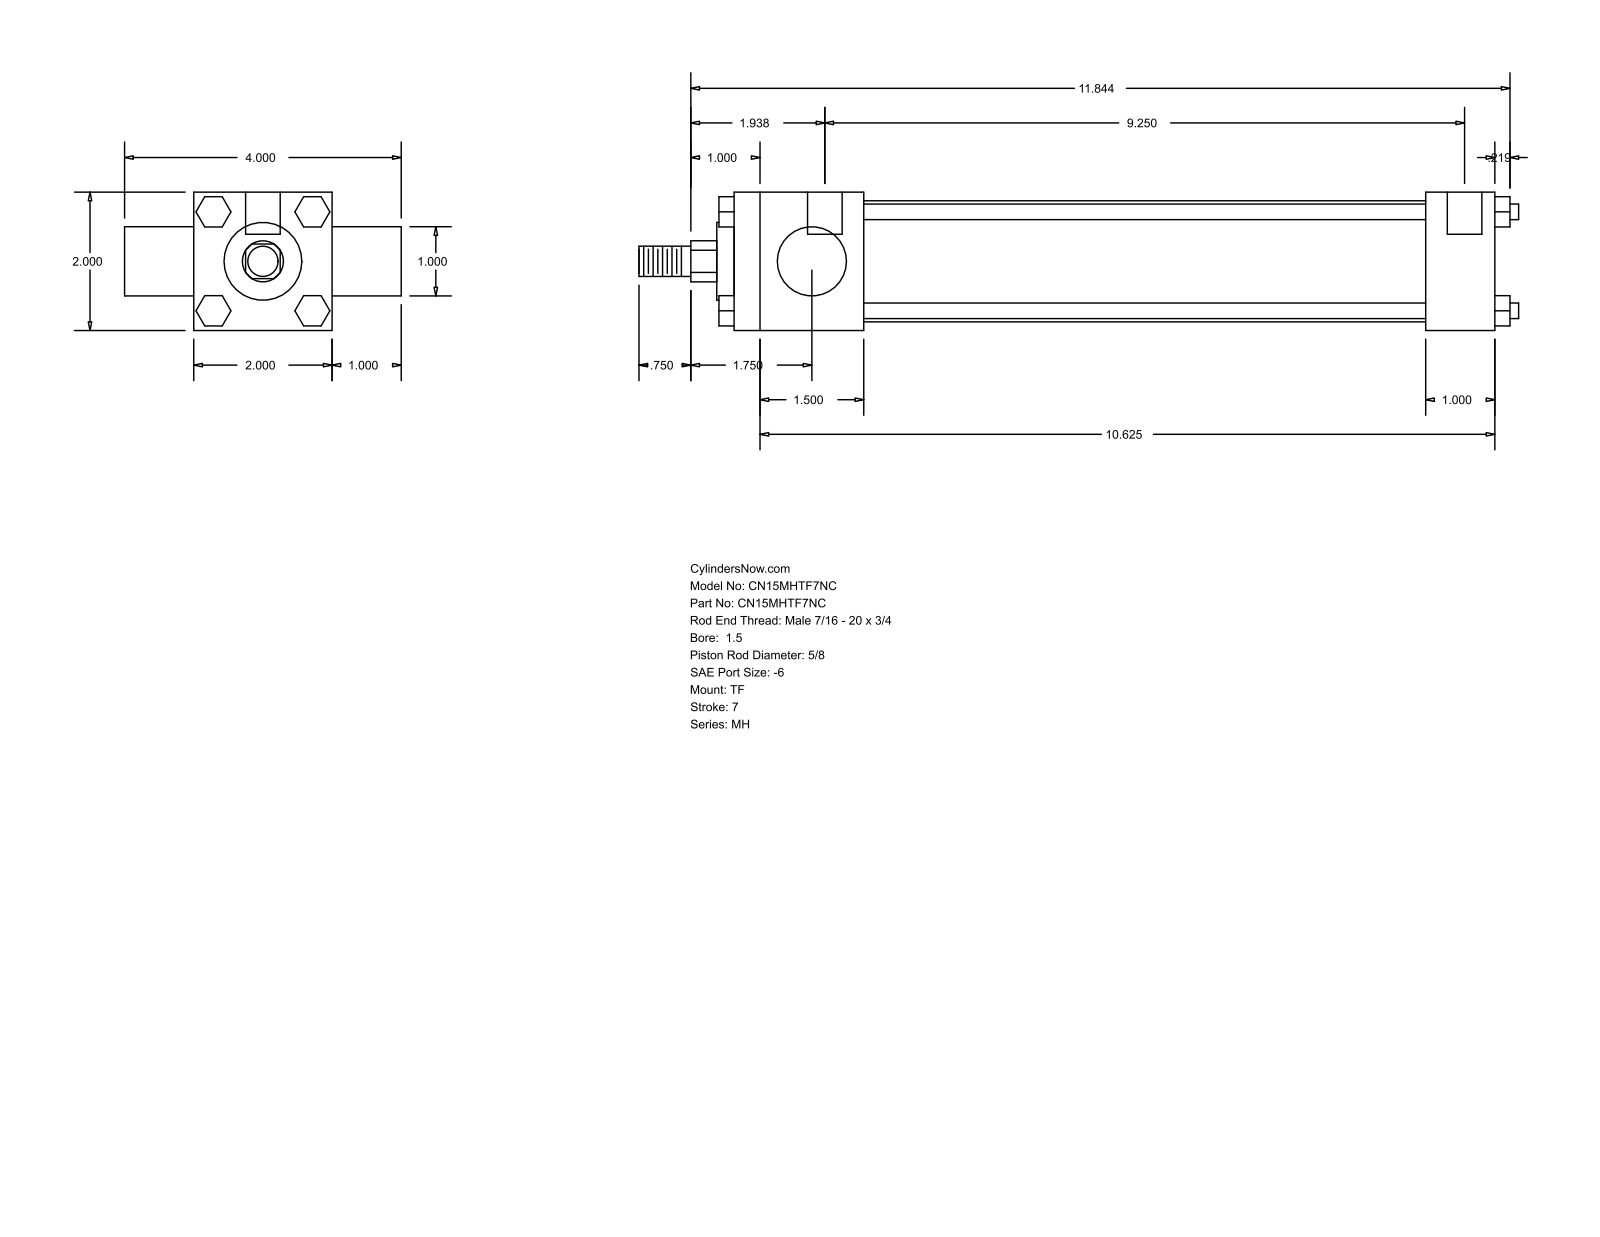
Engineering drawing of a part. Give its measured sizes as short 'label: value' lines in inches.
name: MH_TF__0150_0.625
written by: GSSL Pune (CONFIG_CONTROL_DESIGN)
unit: in
bodies: 0 solids, 120 faces (92 planar, 28 cylindrical, 0 other)
size: 12.719 × 4 × 2
holes: 3× ⌀0.219, 2× ⌀0.5
bosses: 4× ⌀0.225, 1× ⌀1.75, 1× ⌀1.125, 1× ⌀1, 1× ⌀0.625, 1× ⌀0.437
rounds: 1× R0.297
face distances: 2, 11, 1, 3, 1.875, 9.125, 10, 8.125, 1, 0.219
hole spacings: 0.125, 9.25, 9.375
